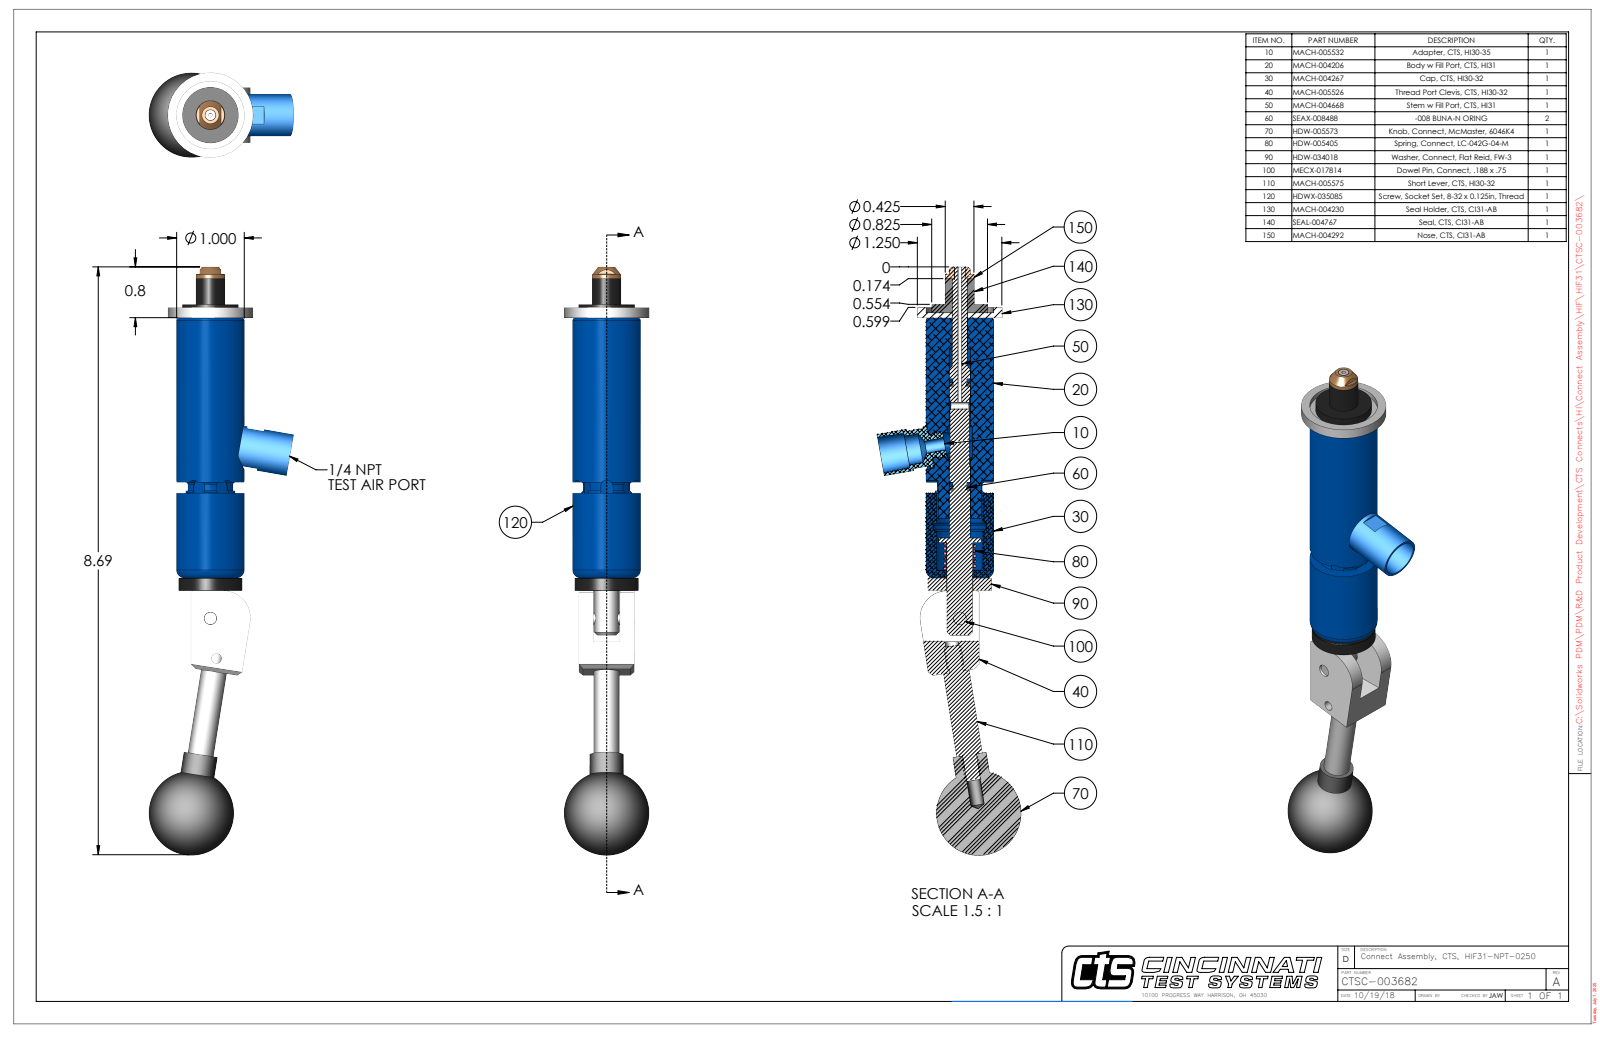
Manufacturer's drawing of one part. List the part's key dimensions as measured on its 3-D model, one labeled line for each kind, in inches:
Part name (STEP PRODUCT): CTSC-003682-C
STEP written by: SolidWorks 2023 (AUTOMOTIVE_DESIGN)
Units: inches
Bodies: 9 solids, 305 faces (114 planar, 128 cylindrical, 63 other)
Overall size (bounding box): 8.692 × 2.128 × 1.25
Volume: 5.216 in³ · Surface area: 41.95 in²
Round holes (diameter × count): ⌀0.201 ×2, ⌀0.063 ×1, ⌀0.109 ×1, ⌀0.136 ×1, ⌀0.15 ×1, ⌀0.159 ×1, ⌀0.187 ×1, ⌀0.189 ×1, ⌀0.218 ×1, ⌀0.228 ×1, ⌀0.229 ×1, ⌀0.385 ×1
Round bosses / shafts (diameter × count): ⌀1.25 ×1, ⌀1 ×1, ⌀0.936 ×1, ⌀0.825 ×1, ⌀0.62 ×1, ⌀0.5 ×1, ⌀0.427 ×1, ⌀0.424 ×1
Partial cylindrical surfaces — rounded edges, fillets, slot ends (radius × count): R0.093 ×6, R0.029 ×2, R0.061 ×1, R0.325 ×1, R0.375 ×1, R0.4 ×1, R0.471 ×1
Main face-to-face distances: 0.072, 0.21, 0.602, 3.916, 3.844, 0.812, 4.103, 4.031, 0.187, 0.391
Hole centre spacings: 0.599, 1.658, 2.252
